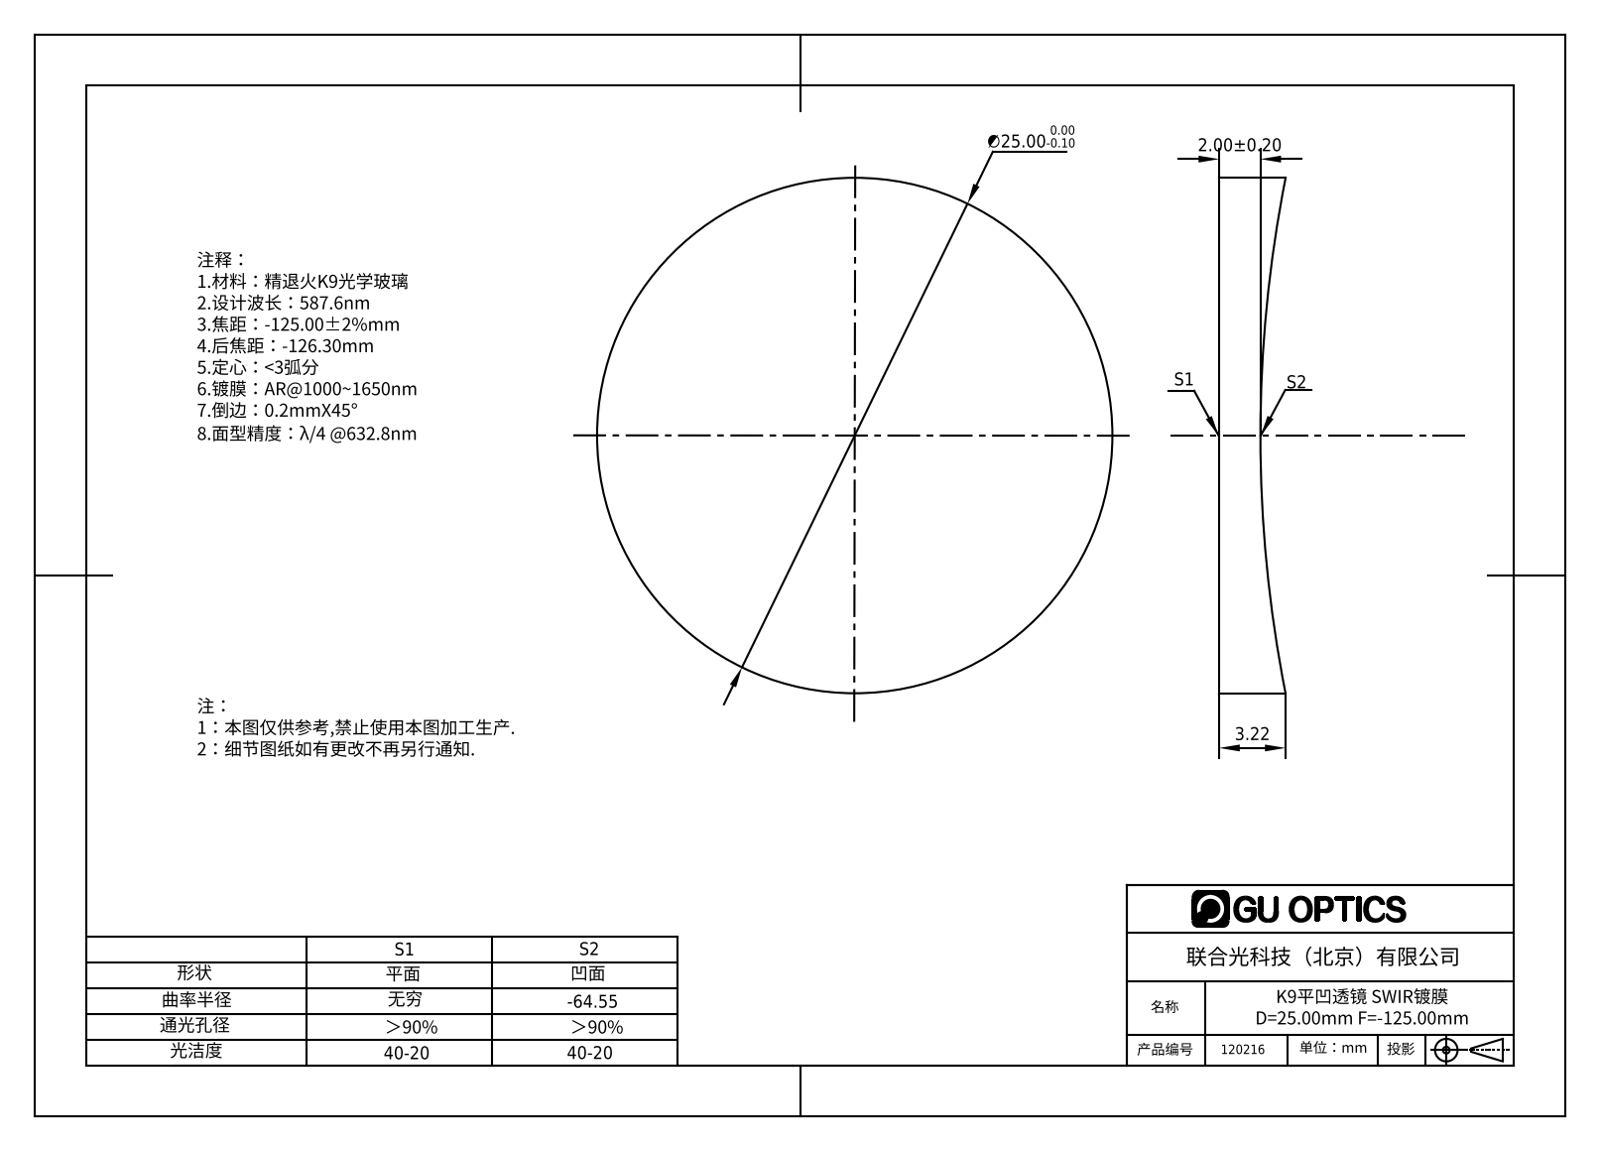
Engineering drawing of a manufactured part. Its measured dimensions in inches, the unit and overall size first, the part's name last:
Units: inches
Overall size (bounding box): 0.984 × 0.984 × 0.127
Round bosses / shafts (diameter × count): ⌀0.984 ×1
Volume: 0.078 in³ · Surface area: 1.922 in²
Bodies: 1 solid, 5 faces (1 planar, 2 cylindrical, 2 other)
Part name (STEP PRODUCT): 120156
STEP written by: SolidWorks 2016 (AUTOMOTIVE_DESIGN)
